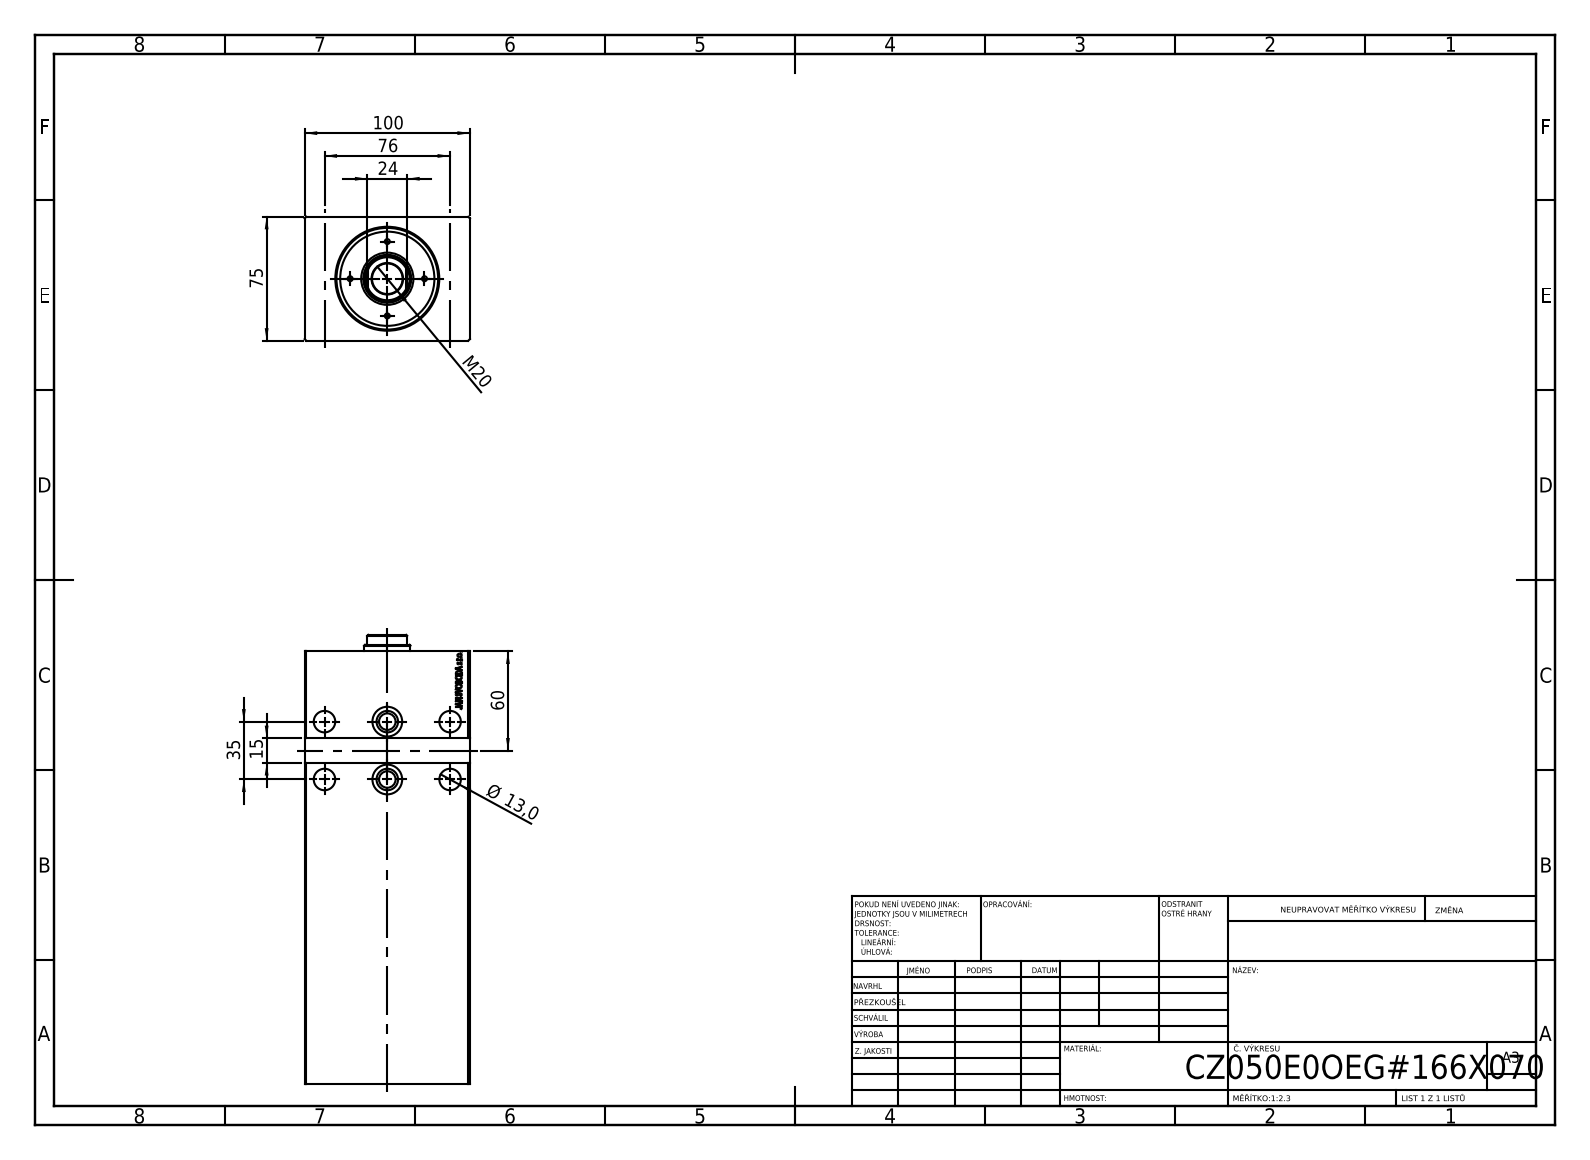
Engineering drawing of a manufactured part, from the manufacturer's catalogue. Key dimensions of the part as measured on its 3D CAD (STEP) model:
STEP written by: SolidWorks 2019 (CONFIG_CONTROL_DESIGN)
Units: millimetres
Bodies: 1 solid, 807 faces (395 planar, 30 cylindrical, 382 other)
Overall size (bounding box): 262 × 100 × 75
Volume: 1 431 000 mm³ · Surface area: 157 040 mm²
Round holes (diameter × count): ⌀13 ×4, ⌀8 ×2, ⌀10 ×2, ⌀18 ×2, ⌀36 ×1, ⌀50 ×1, ⌀61.5 ×1
Round bosses / shafts (diameter × count): ⌀13 ×2
Main face-to-face distances: 75, 100, 262, 244.2, 17.8, 2, 73, 261.8, 17.6, 10
Hole centre spacings: 38, 51.66, 35, 76, 83.67, 18.82, 20.74, 44.32
